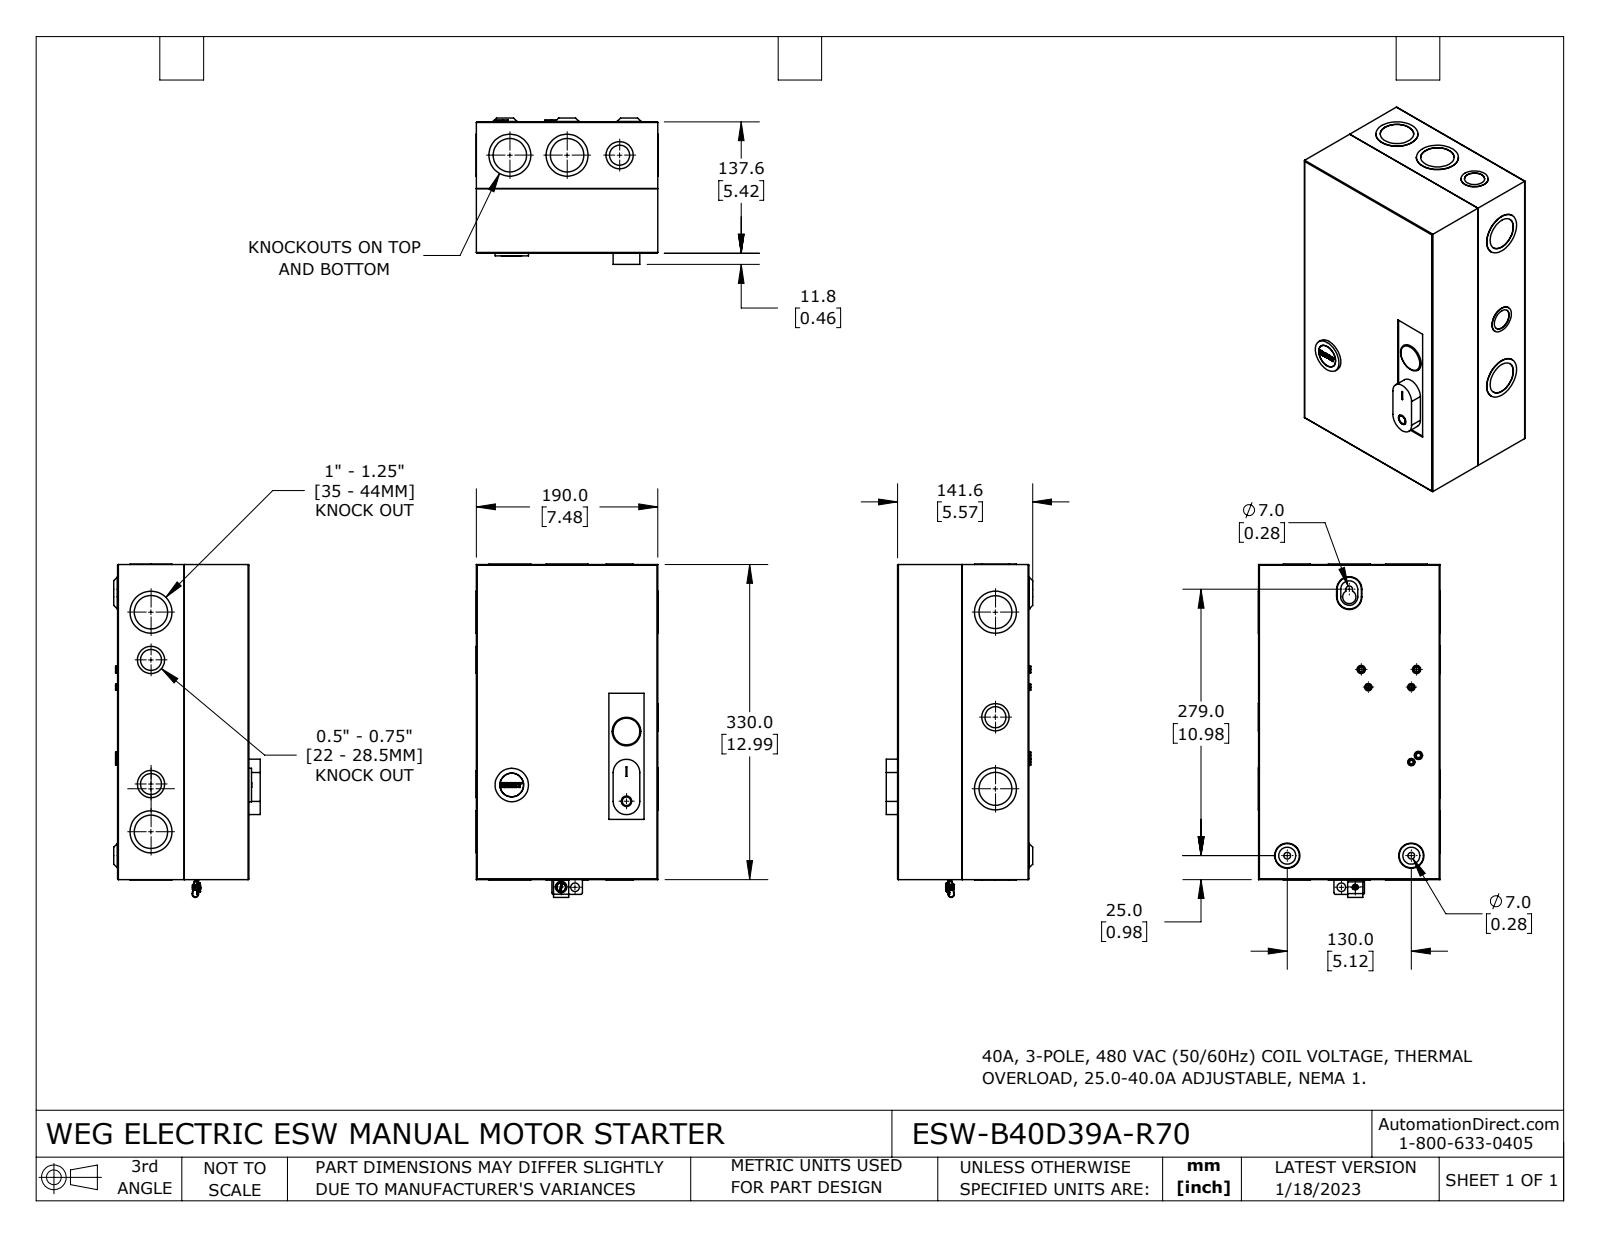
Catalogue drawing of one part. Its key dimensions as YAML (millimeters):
part_name: "ESW-B40D39A-R70"
step_written_by: "SolidWorks 2021 (CONFIG_CONTROL_DESIGN)"
units: millimeters
bodies: {solids: 7, faces: 435, planar: 161, cylindrical: 221, other: 53}
overall_size: [349, 190.6, 153.4]
volume: 402800
surface_area: 604300
round_holes:
  - {diameter: 35, count: 4}
  - {diameter: 3.7, count: 3}
  - {diameter: 4.6, count: 3}
  - {diameter: 7, count: 2}
  - {diameter: 22, count: 2}
  - {diameter: 22.5, count: 2}
  - {diameter: 34.5, count: 2}
  - {diameter: 6.5, count: 1}
  - {diameter: 7.1, count: 1}
  - {diameter: 9, count: 1}
  - {diameter: 11, count: 1}
  - {diameter: 11.9, count: 1}
round_bosses_or_shafts:
  - {diameter: 44, count: 4}
  - {diameter: 28.5, count: 3}
  - {diameter: 7.1, count: 3}
  - {diameter: 6.1, count: 3}
  - {diameter: 44, count: 2}
  - {diameter: 35, count: 1}
  - {diameter: 30.3, count: 1}
  - {diameter: 29.2, count: 1}
partial_cylinders:
  - {radius: 0.1, count: 34}
  - {radius: 0.8, count: 8}
  - {radius: 2, count: 3}
  - {radius: 3.5, count: 3}
  - {radius: 1.5, count: 2}
  - {radius: 1.9, count: 2}
  - {radius: 2.7, count: 2}
  - {radius: 3.1, count: 2}
face_to_face_distances: [1.2, 136.4, 188.8, 135.2, 137.6, 328.8, 187.6, 190, 1.8, 327.6]
hole_center_spacings: [14.5, 45, 50, 58, 60, 130, 180, 278.7]
